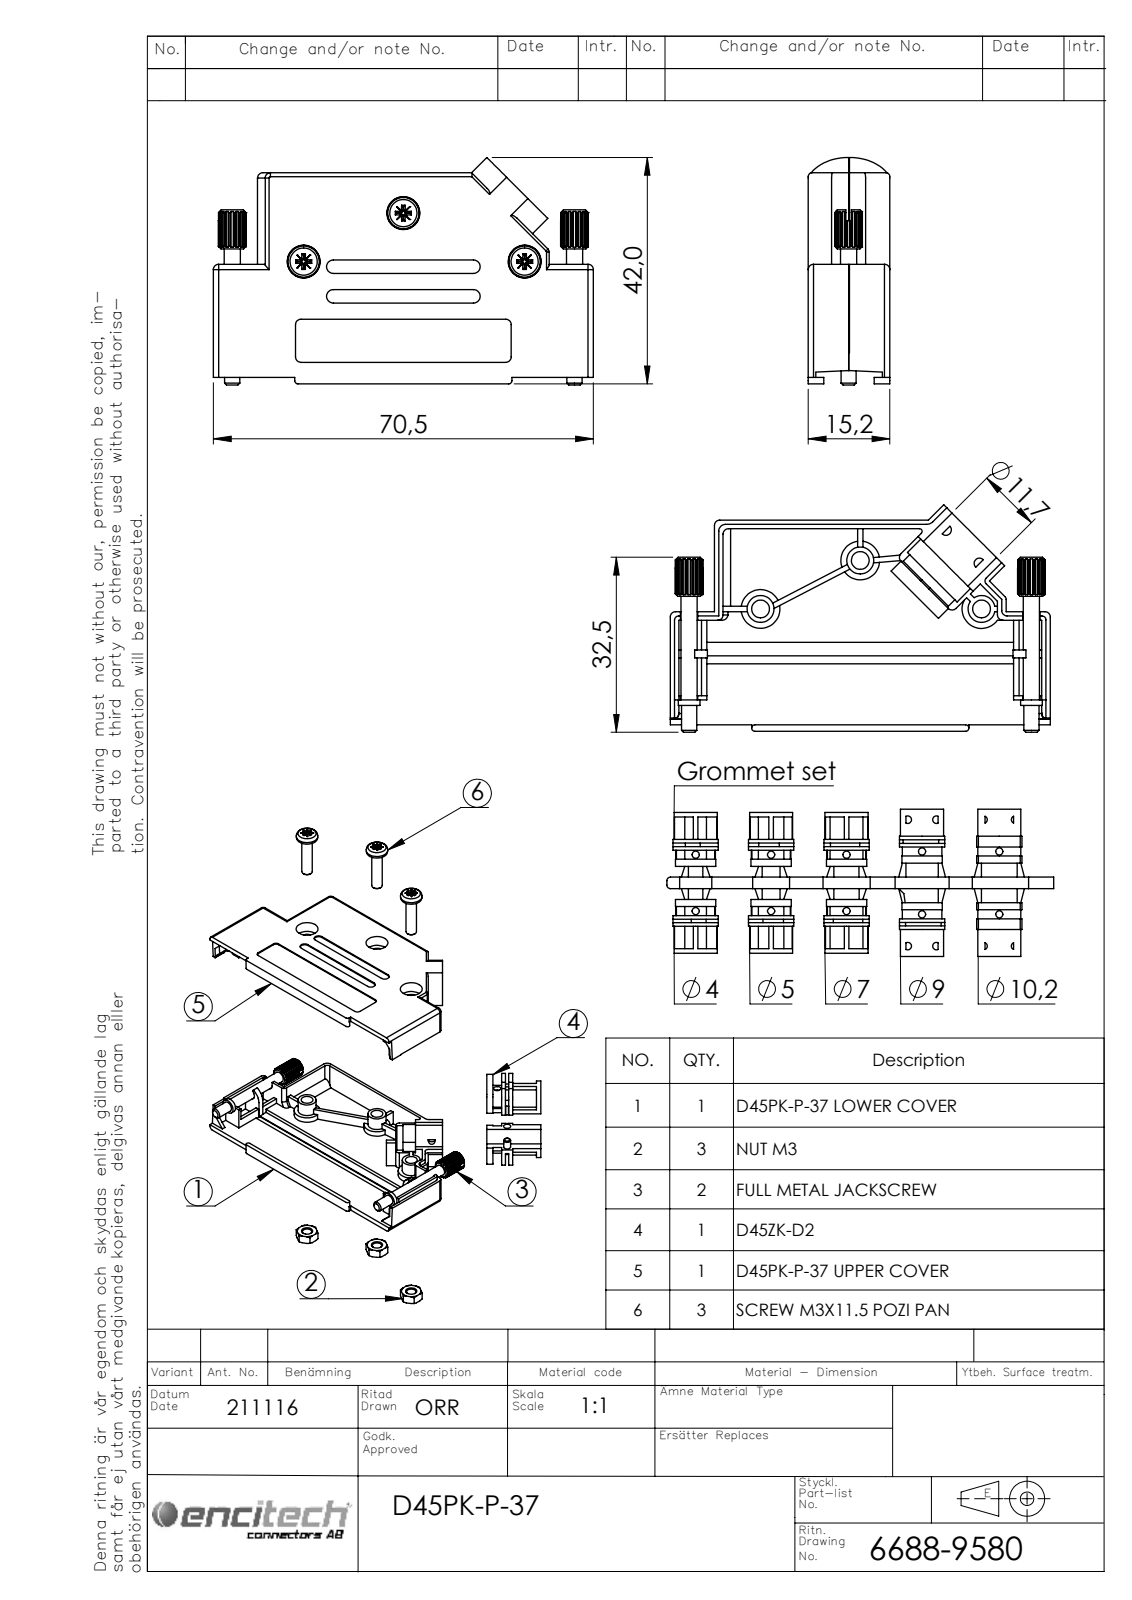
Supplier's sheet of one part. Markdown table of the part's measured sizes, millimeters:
| quantity | value |
| --- | --- |
| part name | 6688-9580; 6855-0303-11; 6805-0102-14; 6826-0141-01 (+3 more) |
| STEP written by | SolidWorks 2021 (AUTOMOTIVE_DESIGN) |
| units | millimeters |
| bodies | 12 solids, 1083 faces (650 planar, 285 cylindrical, 148 other) |
| overall size | 70.5 × 42.23 × 15.15 |
| volume | 12 939 mm³ |
| surface area | 19 625 mm² |
| round holes (diameter × count) | 2 × 3, 2.6 × 3, 3.3 × 3, 6.1 × 3, 7 × 1, 11.7 × 1 |
| round bosses / shafts (diameter × count) | 5 × 3, 2.9 × 3, 7.2 × 2, 4 × 2, 3 × 2, 2.8 × 2, 1.9 × 2, 11.6 × 1 |
| partial cylindrical surfaces (radius × count) | 1 × 26, 0.5 × 13, 0.1 × 12, 0.75 × 8, 1.25 × 5, 1.6 × 4, 5.64 × 4, 5.91 × 4 |
| main face-to-face distances | 1.4, 13.75, 15.15, 12.35, 1, 1.6, 1.1, 2.4, 2.1, 14.85 |
| hole center spacings | 5.71, 5.67, 10.01, 11.11, 11.16, 13.16, 15.65, 18.87 |
